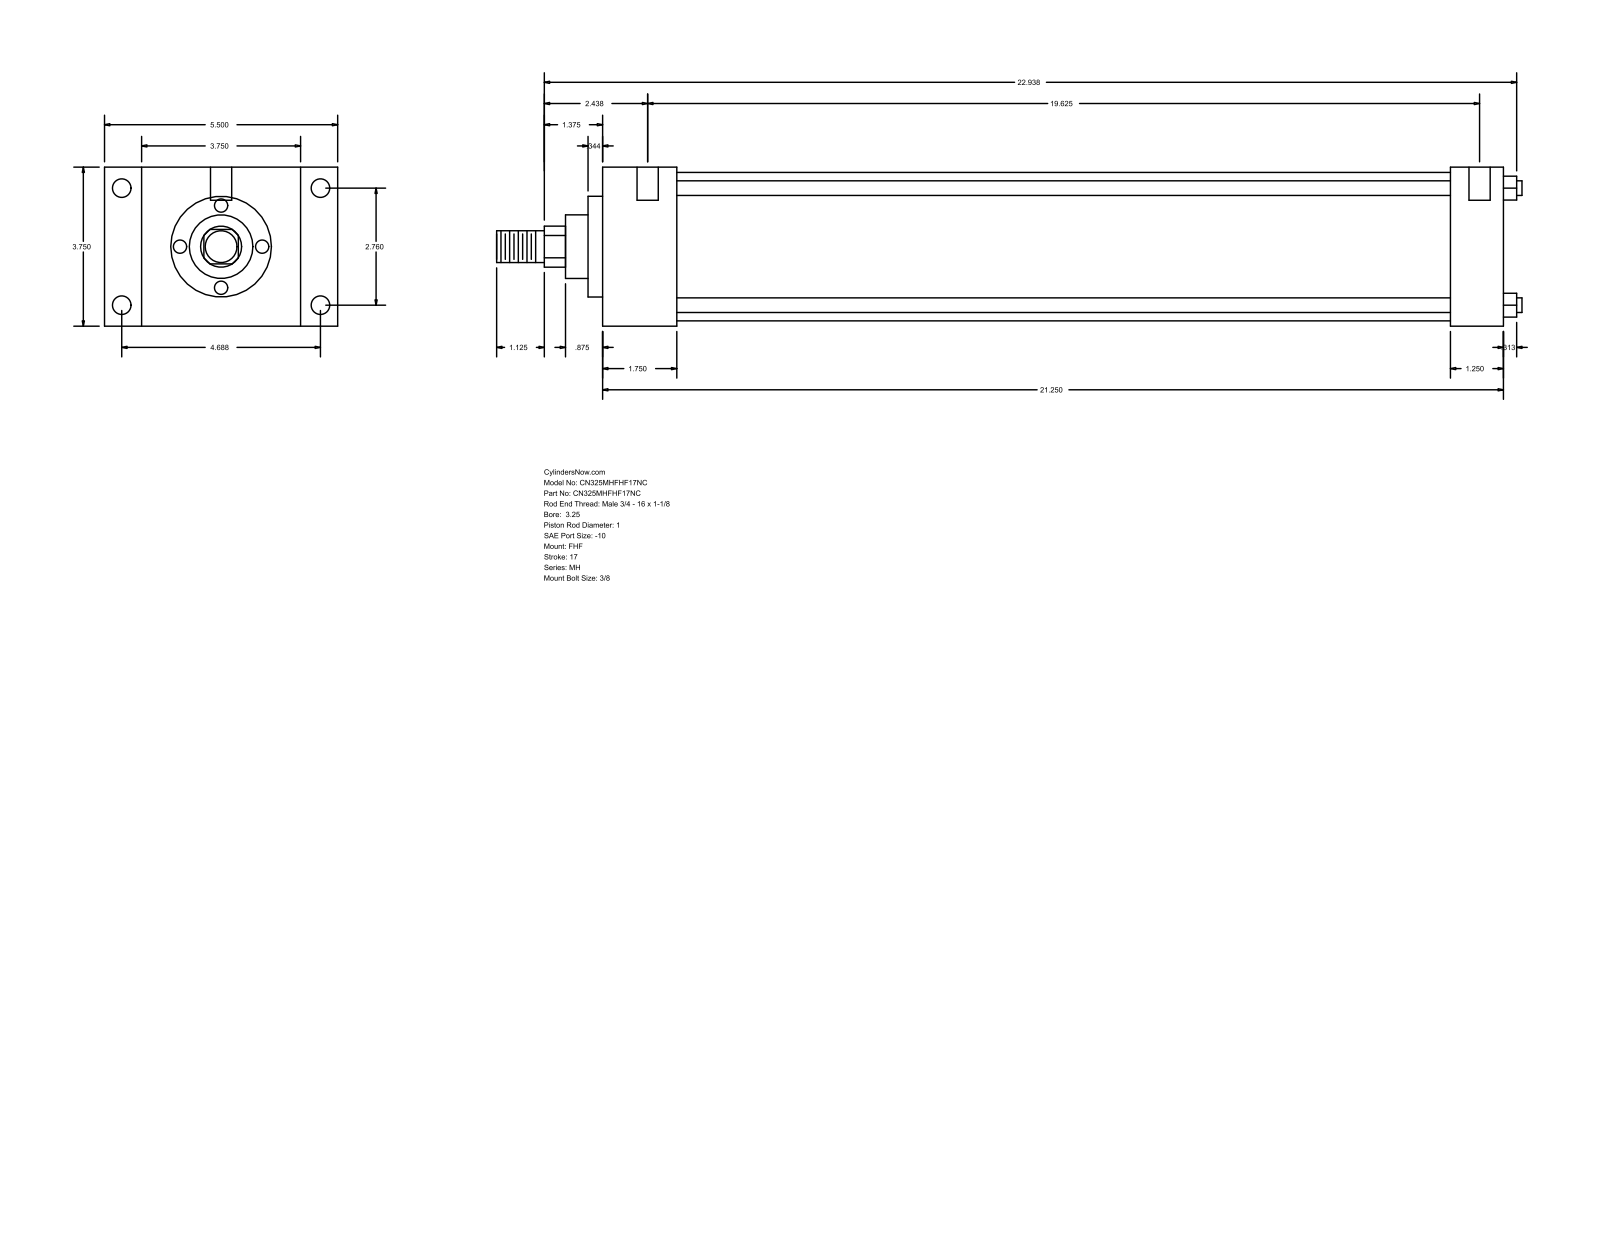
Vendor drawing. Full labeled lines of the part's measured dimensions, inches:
Part name (STEP PRODUCT): MH_FHF__0325_1
STEP written by: GSSL Pune (CONFIG_CONTROL_DESIGN)
Units: inches
Bodies: 0 solids, 90 faces (61 planar, 29 cylindrical, 0 other)
Overall size (bounding box): 24.187 × 5.5 × 3.75
Round holes (diameter × count): ⌀0.219 ×4, ⌀0.438 ×4, ⌀0.5 ×2
Round bosses / shafts (diameter × count): ⌀0.345 ×4, ⌀3.5 ×1, ⌀2.375 ×1, ⌀1.5 ×1, ⌀1 ×1, ⌀0.75 ×1
Partial cylindrical surfaces — rounded edges, fillets, slot ends (radius × count): R0.484 ×1
Main face-to-face distances: 3.75, 21.25, 1.75, 19.5, 0.875, 4.625, 5.5, 20, 18.25, 1.25
Hole centre spacings: 2.76, 4.687, 5.439, 19.875, 0.062, 0.187, 19.625, 19.687
